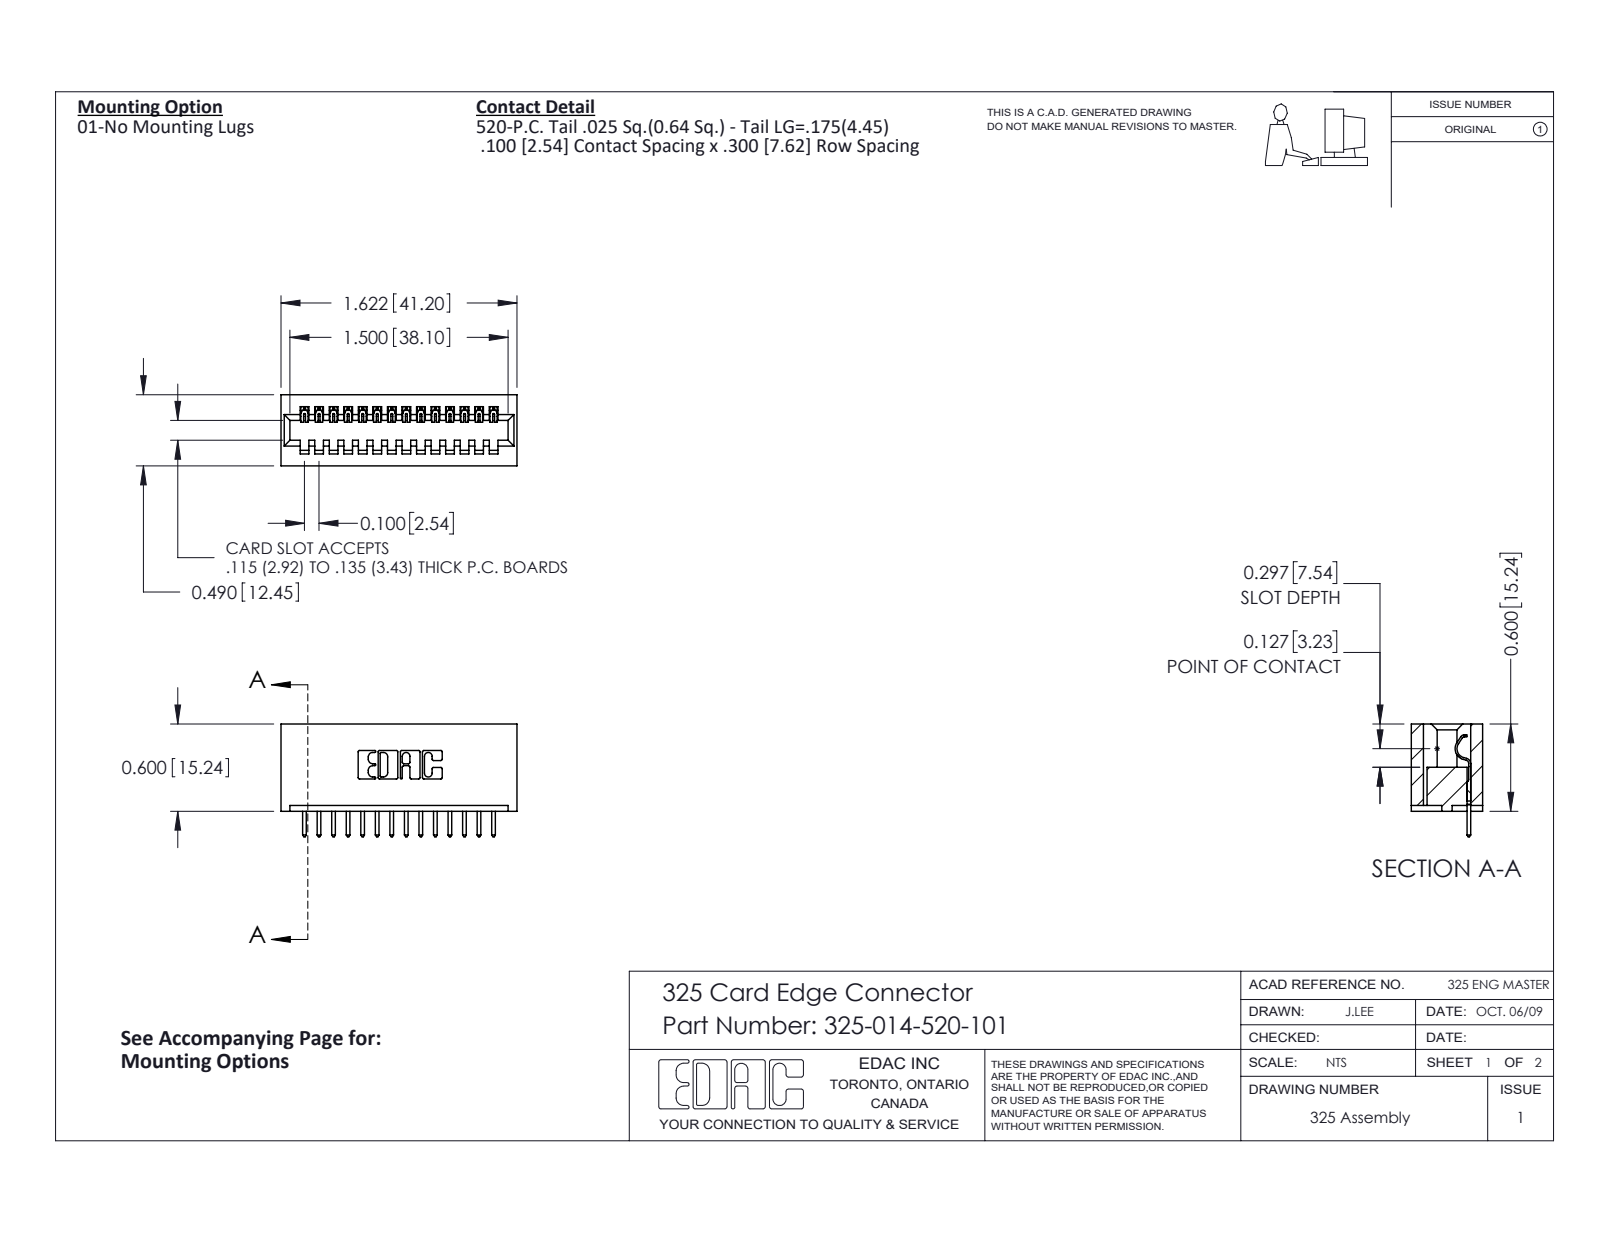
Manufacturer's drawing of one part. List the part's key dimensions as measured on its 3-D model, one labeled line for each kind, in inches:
Part name (STEP PRODUCT): 325-292-001_325-293-120; 325-014-520-101; 325 Part_Lugless
STEP written by: SolidWorks 2016 (CONFIG_CONTROL_DESIGN)
Units: inches
Bodies: 15 solids, 918 faces (654 planar, 264 cylindrical, 0 other)
Overall size (bounding box): 1.622 × 0.775 × 0.49
Volume: 0.338 in³ · Surface area: 9.186 in²
Partial cylindrical surfaces — rounded edges, fillets, slot ends (radius × count): R0.006 ×28, R0.01 ×28, R0.01 ×22, R0.007 ×6, R0.031 ×6, R0.026 ×3, R0.014 ×1, R0.022 ×1
Main face-to-face distances: 0.083, 0.407, 0.3, 0.49, 0.1, 0.2, 0.6, 0.4, 0.56, 0.107
